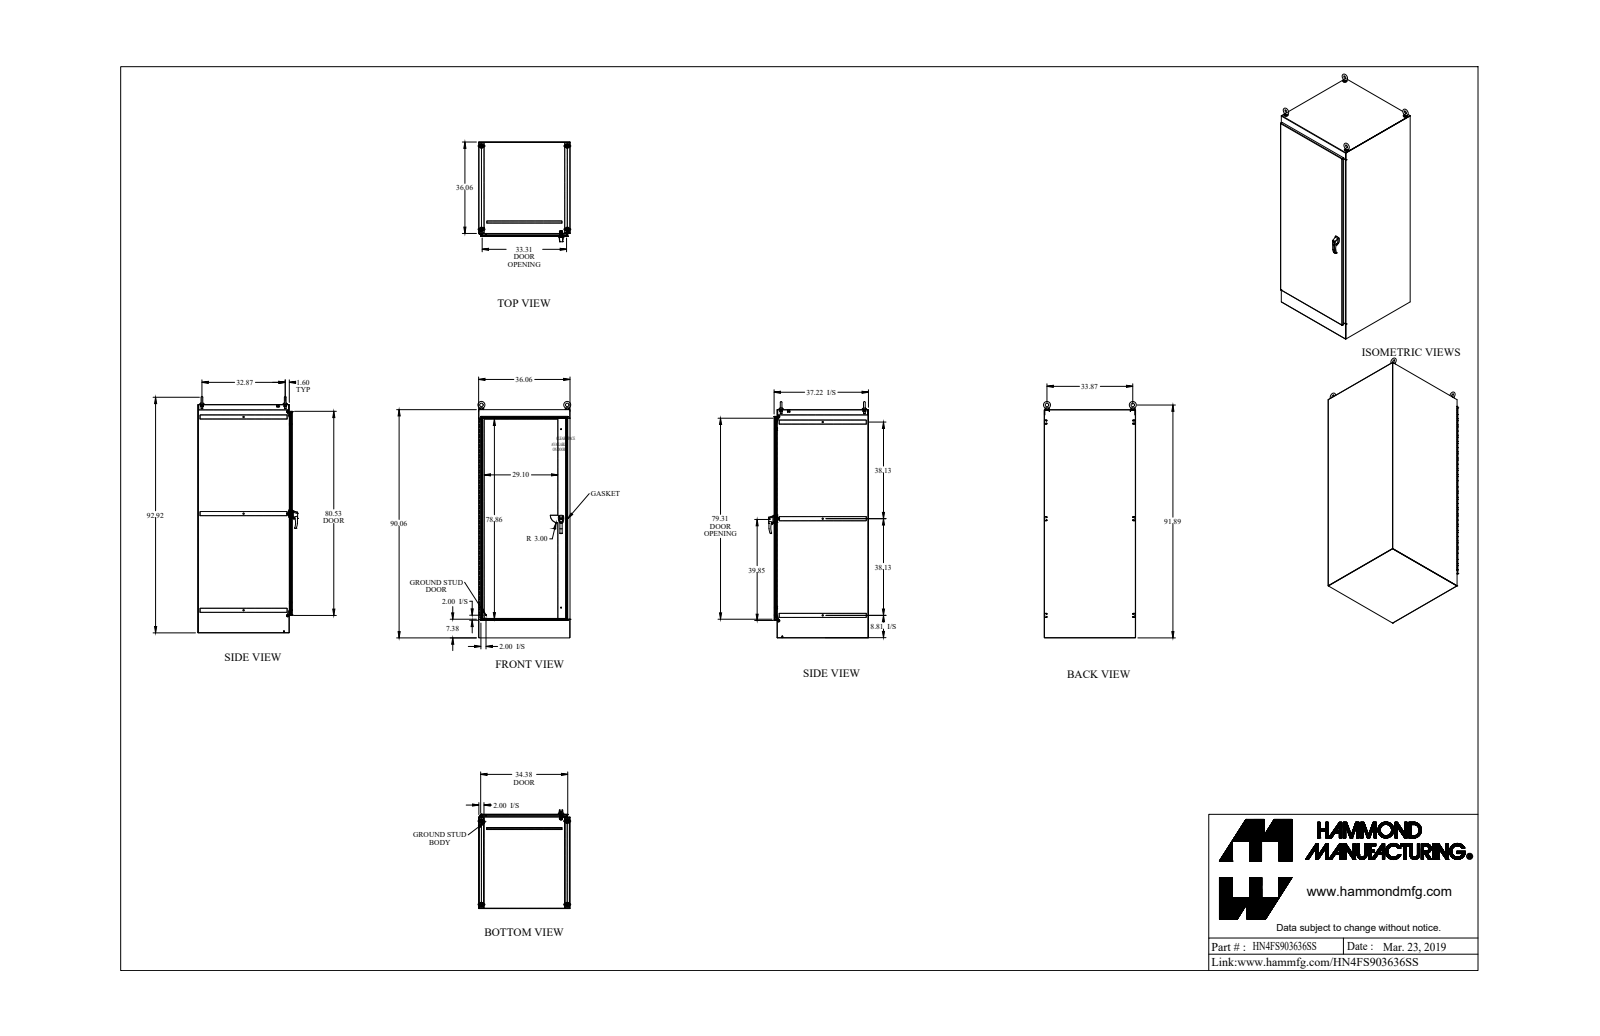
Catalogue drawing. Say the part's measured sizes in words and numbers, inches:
The part is named "HN4FS903636SS". Its 3-D file was written by "SolidWorks 2018 (AUTOMOTIVE_DESIGN)". It is 0 solids with 2173 faces: 951 planar, 981 cylindrical and 241 other. Overall it measures 93.256 by 39.362 by 36.604 inches. Round holes: 13 of diameter 0.304, 7 of diameter 0.35, 6 of diameter 0.75, 4 of diameter 0.527, 4 of diameter 0.625, 4 of diameter 0.68, 3 of diameter 0.5, 2 of diameter 0.25, 2 of diameter 0.257, 2 of diameter 0.28, 2 of diameter 0.281, 2 of diameter 0.313. Round bosses or shafts: 4 of diameter 1.75, 4 of diameter 1.5, 4 of diameter 1.25, 4 of diameter 0.738, 2 of diameter 1, 2 of diameter 0.75, 2 of diameter 0.63, 2 of diameter 0.625. Partial cylindrical surfaces (rounded edges, fillets, slot ends): 42 of radius 0.043, 36 of radius 0.138, 23 of radius 0.5, 22 of radius 0.125, 16 of radius 0.018, 15 of radius 0.06, 13 of radius 0.048, 13 of radius 0.143. The main face-to-face distances are 0.095, 35.965, 37.152, 35.87, 36.06, 37.057, 37.247, 89.965, 89.87, 90.06. The hole center spacings are 6, 12, 18, 24, 30, 36, 42, 33.87.
